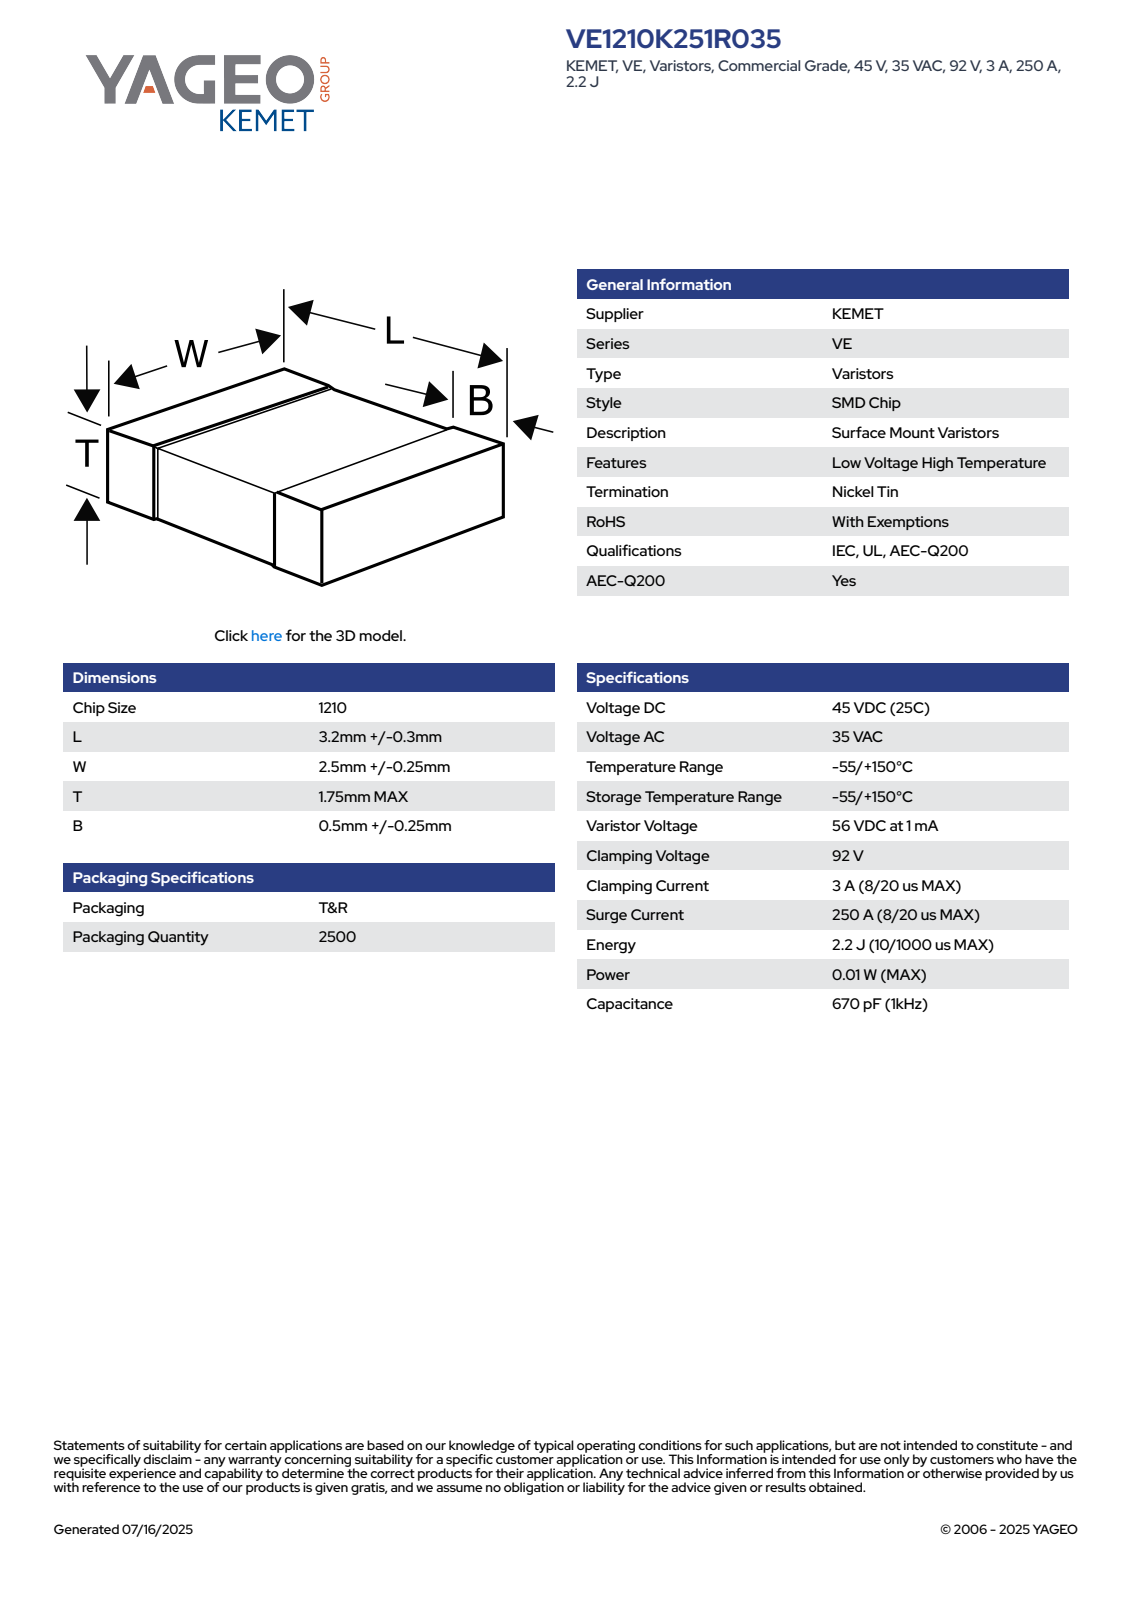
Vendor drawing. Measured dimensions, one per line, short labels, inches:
name: VS_SMD_1210_L3.5W2.75T1.75B0.75
written by: SolidWorks 2021 (AUTOMOTIVE_DESIGN)
unit: in
bodies: 4 solids, 125 faces (71 planar, 38 cylindrical, 16 other)
size: 0.138 × 0.108 × 0.069
volume: 0.001 in³; area: 0.064 in²
face distances: 0.067, 0.064, 0.138, 0.106, 0.069, 0.104, 0.108, 0.065, 0.067, 0.059
